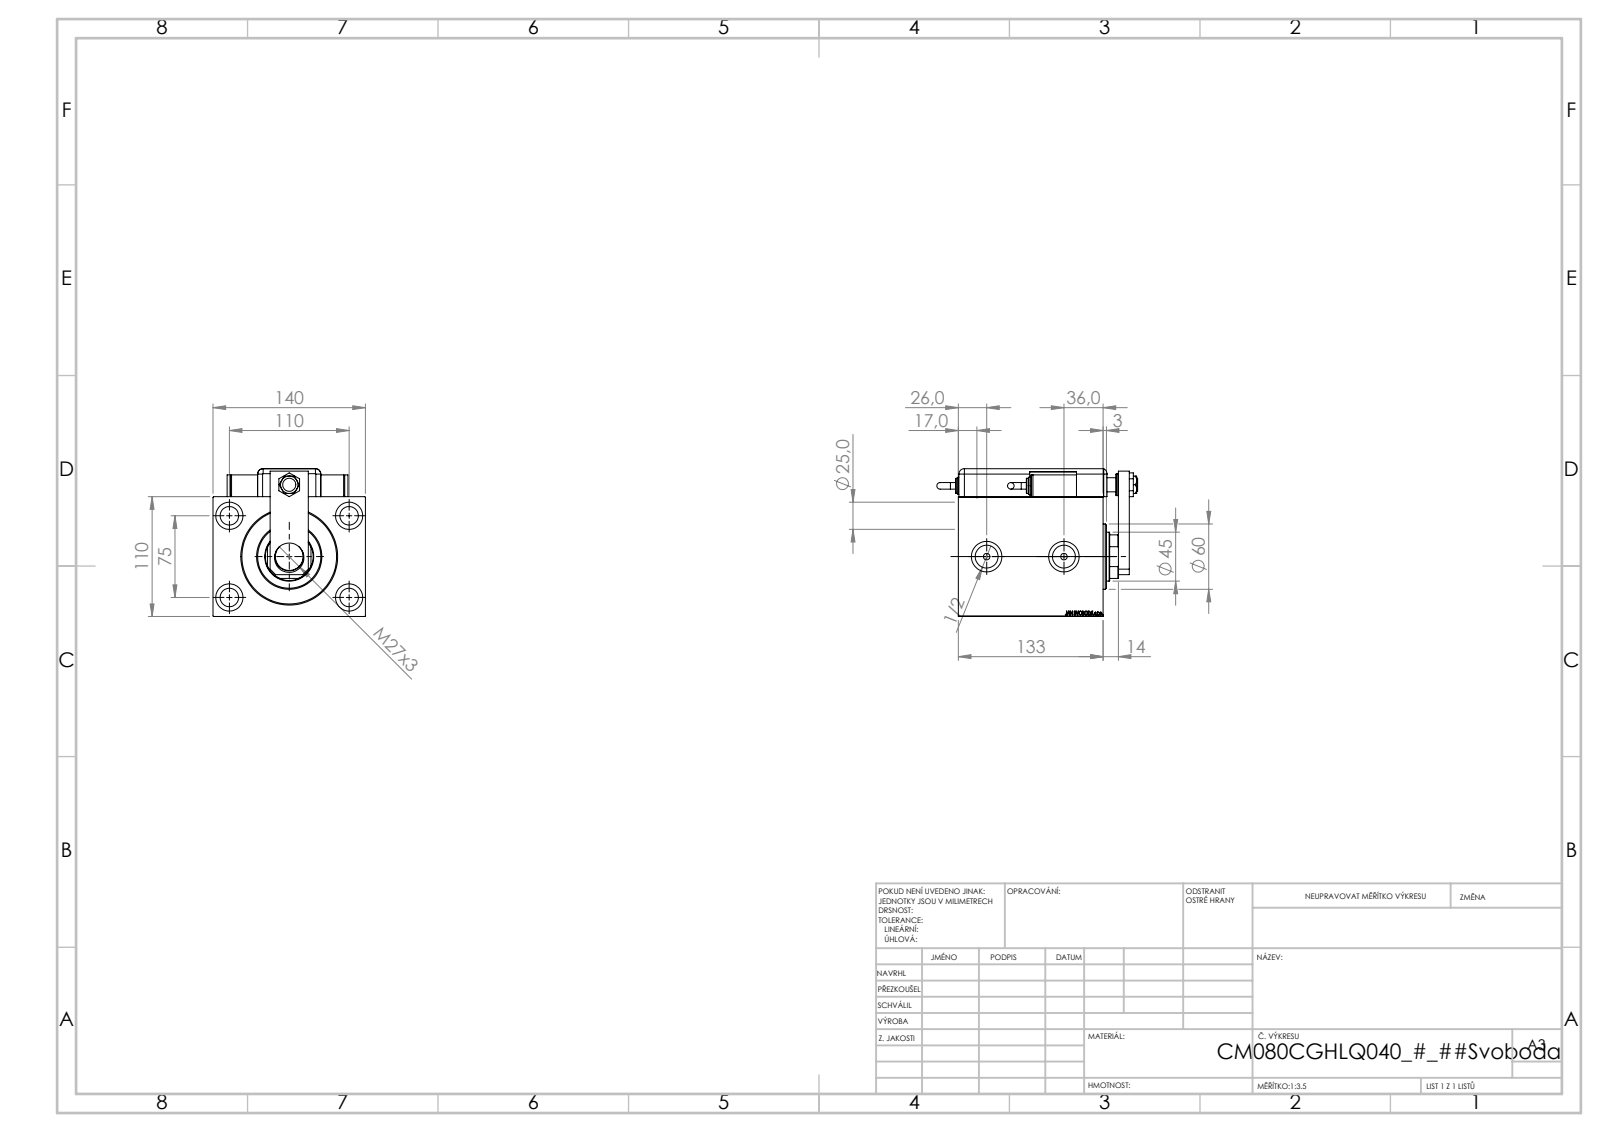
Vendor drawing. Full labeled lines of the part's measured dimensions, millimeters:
Part name (STEP PRODUCT): MAGNETIC SWITCH Q; ZARAZKA_Q; SWITCH Q; KRYT (+7 more)
STEP written by: SolidWorks 2019 (CONFIG_CONTROL_DESIGN)
Units: millimetres
Bodies: 13 solids, 1246 faces (614 planar, 115 cylindrical, 517 other)
Overall size (bounding box): 184.46 × 140 × 135.8
Volume: 1 919 000 mm³ · Surface area: 275 303 mm²
Round holes (diameter × count): ⌀17 ×4, ⌀25 ×4, ⌀4 ×2, ⌀6 ×2, ⌀8 ×2, ⌀20.96 ×2, ⌀28 ×2, ⌀12 ×1, ⌀13 ×1, ⌀14 ×1, ⌀25.5 ×1, ⌀27 ×1
Round bosses / shafts (diameter × count): ⌀20 ×3, ⌀16 ×2, ⌀14 ×2, ⌀6 ×2, ⌀60 ×1
Partial cylindrical surfaces — rounded edges, fillets, slot ends (radius × count): R5 ×9, R10 ×1, R22 ×1
Main face-to-face distances: 110, 140, 3, 133, 21, 112, 14, 28, 25.8, 135.8
Hole centre spacings: 66.57, 61.95, 66.01, 67.14, 75, 110, 117.21, 133.14
